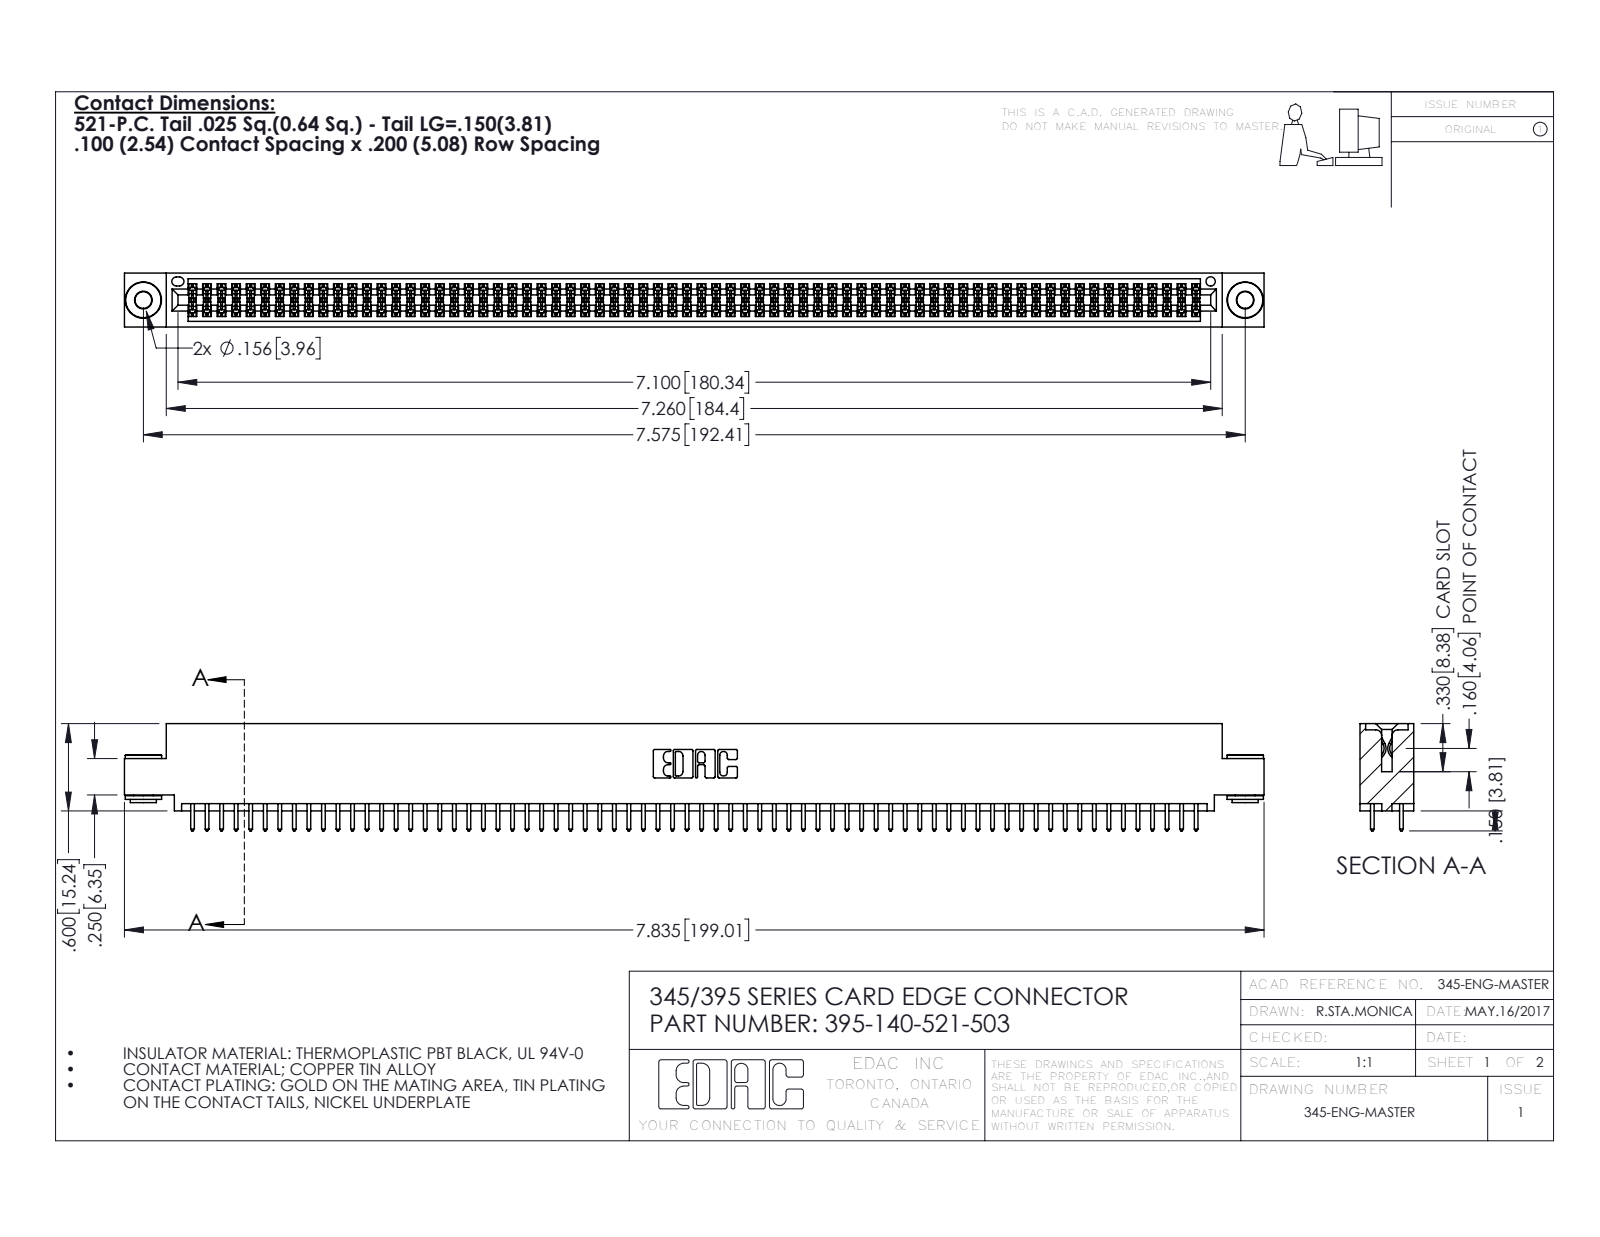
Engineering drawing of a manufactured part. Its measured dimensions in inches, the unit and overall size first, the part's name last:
Units: inches
Overall size (bounding box): 7.835 × 0.737 × 0.37
Round holes (diameter × count): ⌀0.116 ×2, ⌀0.156 ×2, ⌀0.064 ×1
Round bosses / shafts (diameter × count): ⌀0.25 ×2, ⌀0.18 ×2, ⌀0.136 ×2
Partial cylindrical surfaces — rounded edges, fillets, slot ends (radius × count): R0.006 ×210, R0.01 ×140, R0.01 ×22, R0.007 ×6, R0.031 ×6, R0.026 ×3, R0.014 ×2, R0.019 ×2
Main face-to-face distances: 0.072, 0.298, 0.2, 0.025, 0.098, 0.272, 0.37, 0.225, 0.175, 0.149
Hole centre spacings: 0.27, 7.339, 7.575
Volume: 1.189 in³ · Surface area: 45.36 in²
Bodies: 143 solids, 7168 faces (4714 planar, 2446 cylindrical, 8 other)
Part name (STEP PRODUCT): 395-140-521-503; 345 Part_0.110 Offset - 0.156 Dia-TH; 345-250-002_345-250-002-102; 345-292-001_345-293-121
STEP written by: SolidWorks 2016 (CONFIG_CONTROL_DESIGN)
